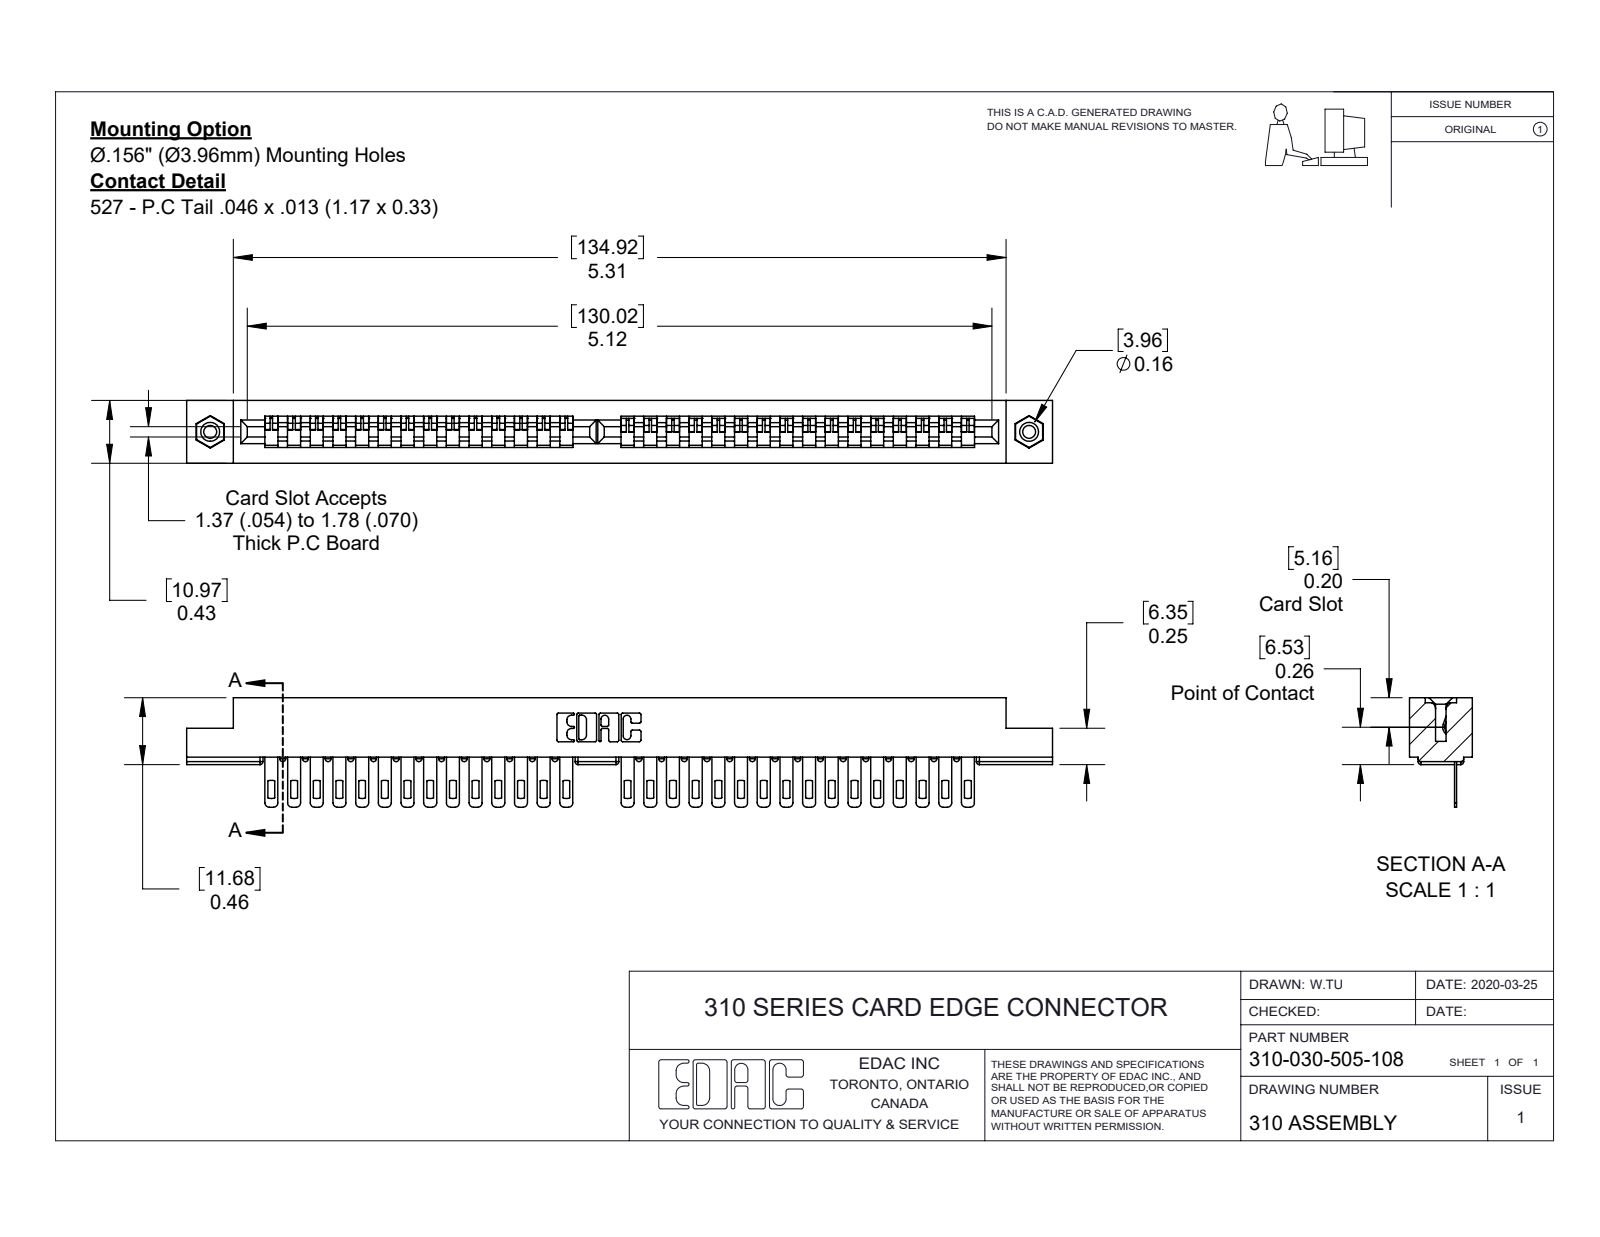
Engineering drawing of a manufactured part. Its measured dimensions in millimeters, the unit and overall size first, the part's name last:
Units: millimetres
Overall size (bounding box): 151.21 × 19.13 × 10.97
Round holes (diameter × count): ⌀2.26 ×2, ⌀3.17 ×2, ⌀3.96 ×2
Round bosses / shafts (diameter × count): ⌀3.94 ×2
Partial cylindrical surfaces — rounded edges, fillets, slot ends (radius × count): R0.51 ×98, R0.76 ×60, R1.59 ×30, R0.25 ×22, R0.17 ×6, R0.8 ×6, R0.67 ×3, R0.3 ×2
Main face-to-face distances: 2.76, 8.22, 10.98, 0.38, 0.33, 1.82, 10.38, 5.08, 5.46, 3.14
Hole centre spacings: 143
Volume: 12 703 mm³ · Surface area: 15 360 mm²
Bodies: 33 solids, 1906 faces (1196 planar, 630 cylindrical, 80 other)
Part name (STEP PRODUCT): 310-030-505-108; 345-250-001_345-250-003-102; 307-290-001_505; 310 Part_.116 Hex
STEP written by: SolidWorks 2016 (CONFIG_CONTROL_DESIGN)
